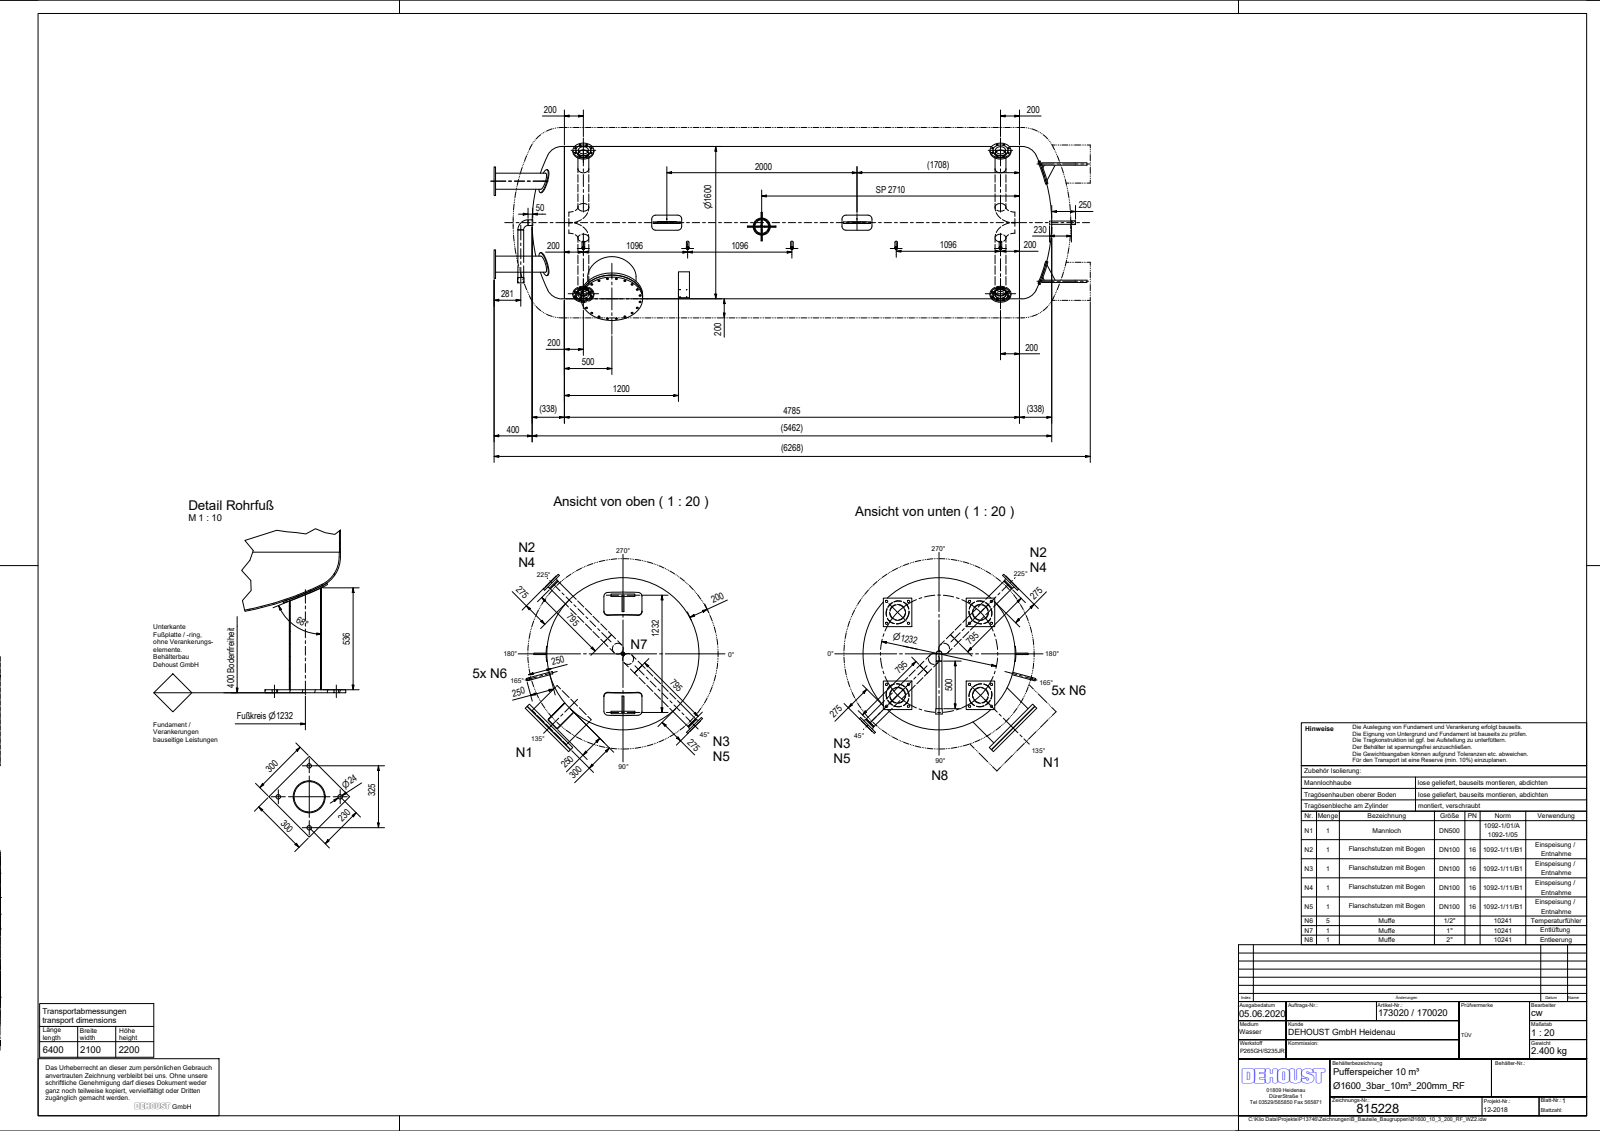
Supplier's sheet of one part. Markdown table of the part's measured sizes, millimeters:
| quantity | value |
| --- | --- |
| part name | Ø1600_10_3_200_RF_WZ2; Klöpper_Gew_Ø1600_6 ,4; Zyl_Ø1600_5x4785; TÖB_Puffer_Ø1600_6,4_200 (+8 more) |
| STEP written by | Autodesk Inventor 2019 (AUTOMOTIVE_DESIGN) |
| units | millimeters |
| bodies | 58 solids, 449 faces (178 planar, 225 cylindrical, 46 other) |
| overall size | 6233.64 × 1863.58 × 1863.58 |
| volume | 269 700 000 mm³ |
| surface area | 70 260 000 mm² |
| round holes (diameter × count) | 22 × 40, 18 × 32, 24 × 16, 18.63 × 5, 21.7 × 5, 26.9 × 5, 5.8 × 4, 106.3 × 4, 107.1 × 4, 159.3 × 4, 5 × 2, 52.3 × 2 |
| round bosses / shafts (diameter × count) | 114.3 × 8, 26.9 × 5, 26.4 × 5, 250 × 4, 220 × 4, 168.3 × 4, 158 × 4, 645 × 2 |
| partial cylindrical surfaces (radius × count) | 42 × 16, 10 × 6, 6 × 4, 5 × 2, 36 × 2, 72 × 2, 125 × 1, 807 × 1 |
| main face-to-face distances | 16, 3017.69, 3212.69, 195, 3033.69, 3228.69, 28, 600, 25, 303.5 |
| hole center spacings | 90, 300, 93.86, 185.41, 1096.25, 4385, 352.67, 485.41 |
